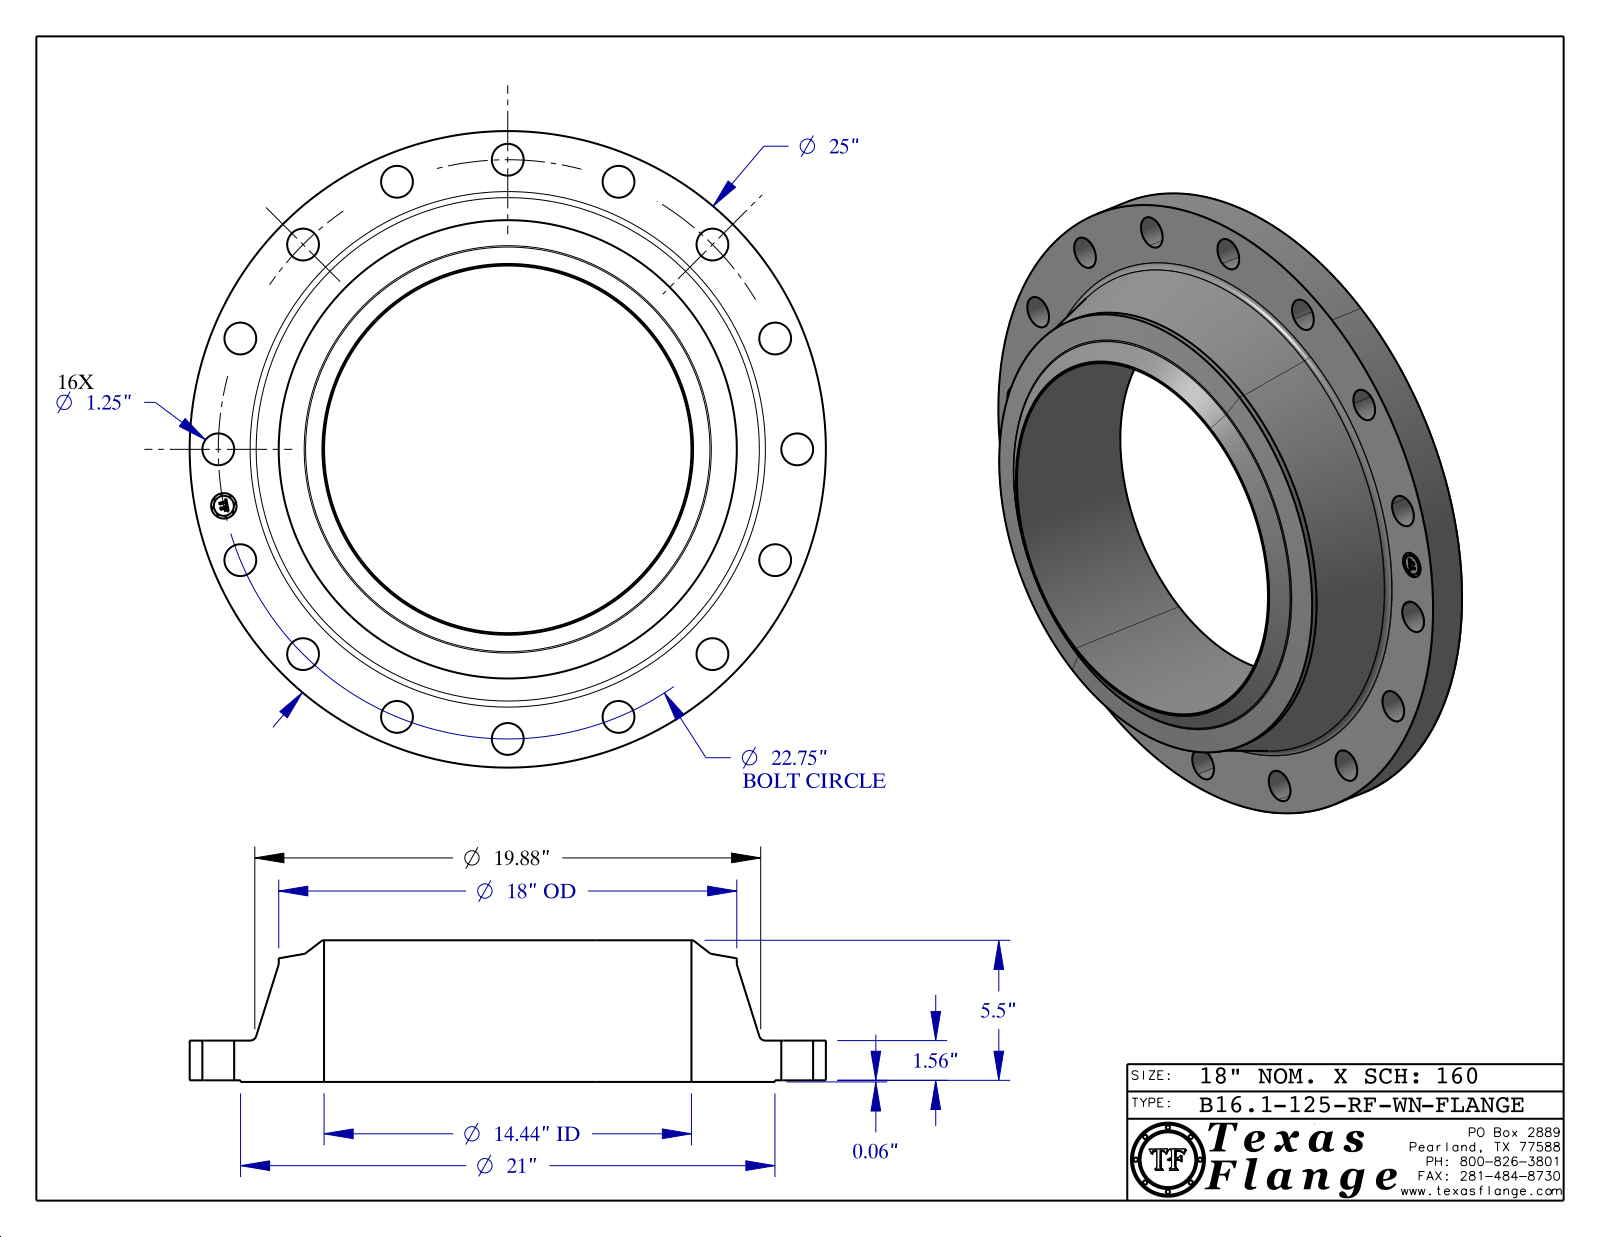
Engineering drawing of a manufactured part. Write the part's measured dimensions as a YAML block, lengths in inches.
part_name: "B16.1, Class 125-RF-WN"
step_written_by: "CATIA V5 STEP AP214 (AUTOMOTIVE_DESIGN)"
units: inches
bodies: {solids: 1, faces: 439, planar: 369, cylindrical: 60, other: 10}
overall_size: [25, 25, 5.563]
volume: 888.6
surface_area: 1243
round_holes:
  - {diameter: 1.25, count: 16}
  - {diameter: 1, count: 1}
  - {diameter: 14.438, count: 1}
round_bosses_or_shafts:
  - {diameter: 0.061, count: 8}
  - {diameter: 25, count: 1}
  - {diameter: 21, count: 1}
  - {diameter: 18, count: 1}
  - {diameter: 0.788, count: 1}
face_to_face_distances: [1.623, 0.063, 1.56, 5.563, 5.5, 3.94, 1.608, 1.545, 0.015, 3.955]
hole_center_spacings: [12.639, 22.313, 11.375, 8.706, 16.087, 21.019, 4.438, 4.439]
